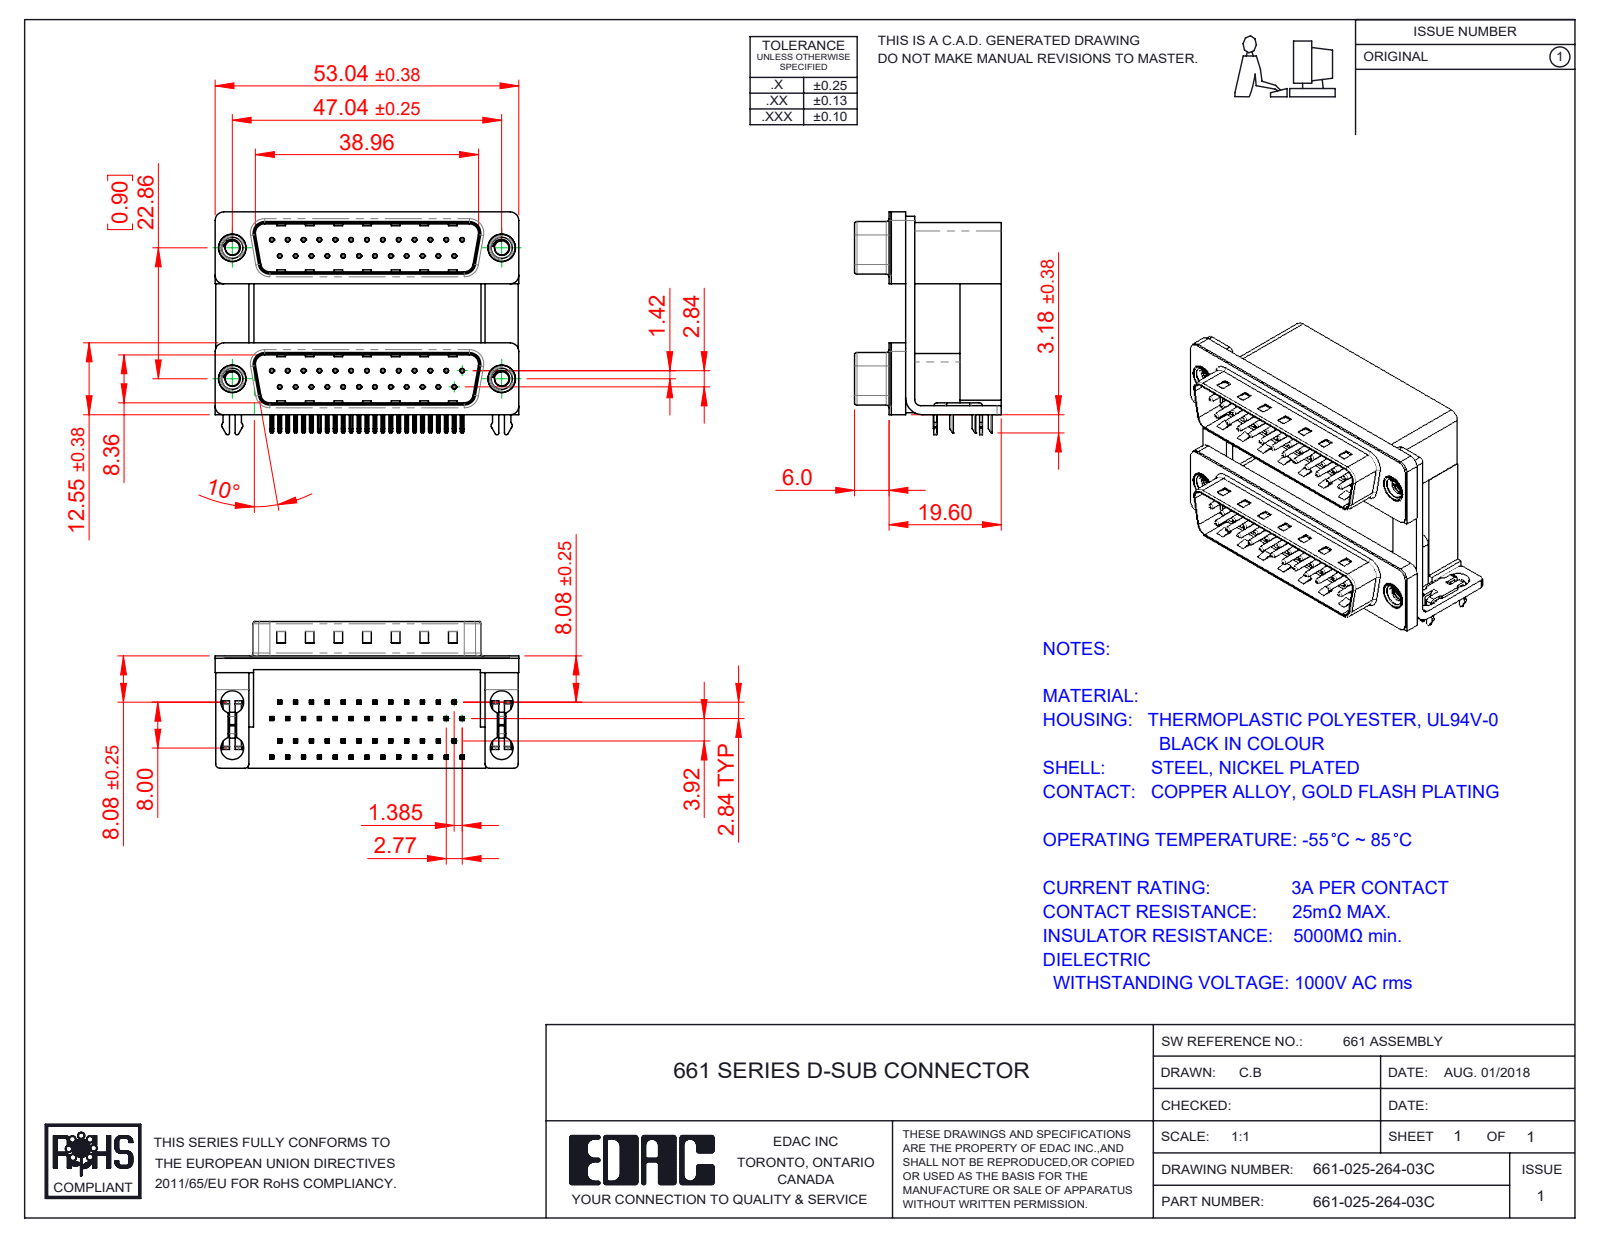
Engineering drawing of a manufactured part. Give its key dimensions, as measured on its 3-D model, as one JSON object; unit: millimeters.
{"part_name": "661 2 Prong Board Lock_3; 661 Mounting Bracket_2ProngH; 661 Shell_25 Contacts; 661 Housing Upper_25 Contacts H (+8 more)", "step_written_by": "SolidWorks 2020 (CONFIG_CONTROL_DESIGN)", "units": "millimeters", "bodies": {"solids": 63, "faces": 4770, "planar": 3040, "cylindrical": 1340, "other": 390}, "overall_size": [53.04, 38.91, 25.6], "volume_mm3": 22355, "surface_area_mm2": 23398, "round_holes": [[0.35, 50], [0.8, 50], [4, 8], [2.5, 4], [3.5, 4], [4.8, 4], [5, 4]], "round_bosses_or_shafts": [[0.75, 50], [4.9, 4], [4.75, 4], [3.9, 4]], "partial_cylinders_radius": [[0.25, 210], [0.12, 100], [0.5, 20], [1.5, 14], [0.75, 10], [0.9, 8], [1.6, 8], [2, 8]], "face_to_face_distances": [12, 22.86, 19.2, 0.4, 7.2, 10.7, 12.4, 16.7, 9.5, 2.5], "hole_center_spacings": [3.16, 2.77, 5.54, 8.31, 11.08, 13.85, 16.62, 5.03]}
